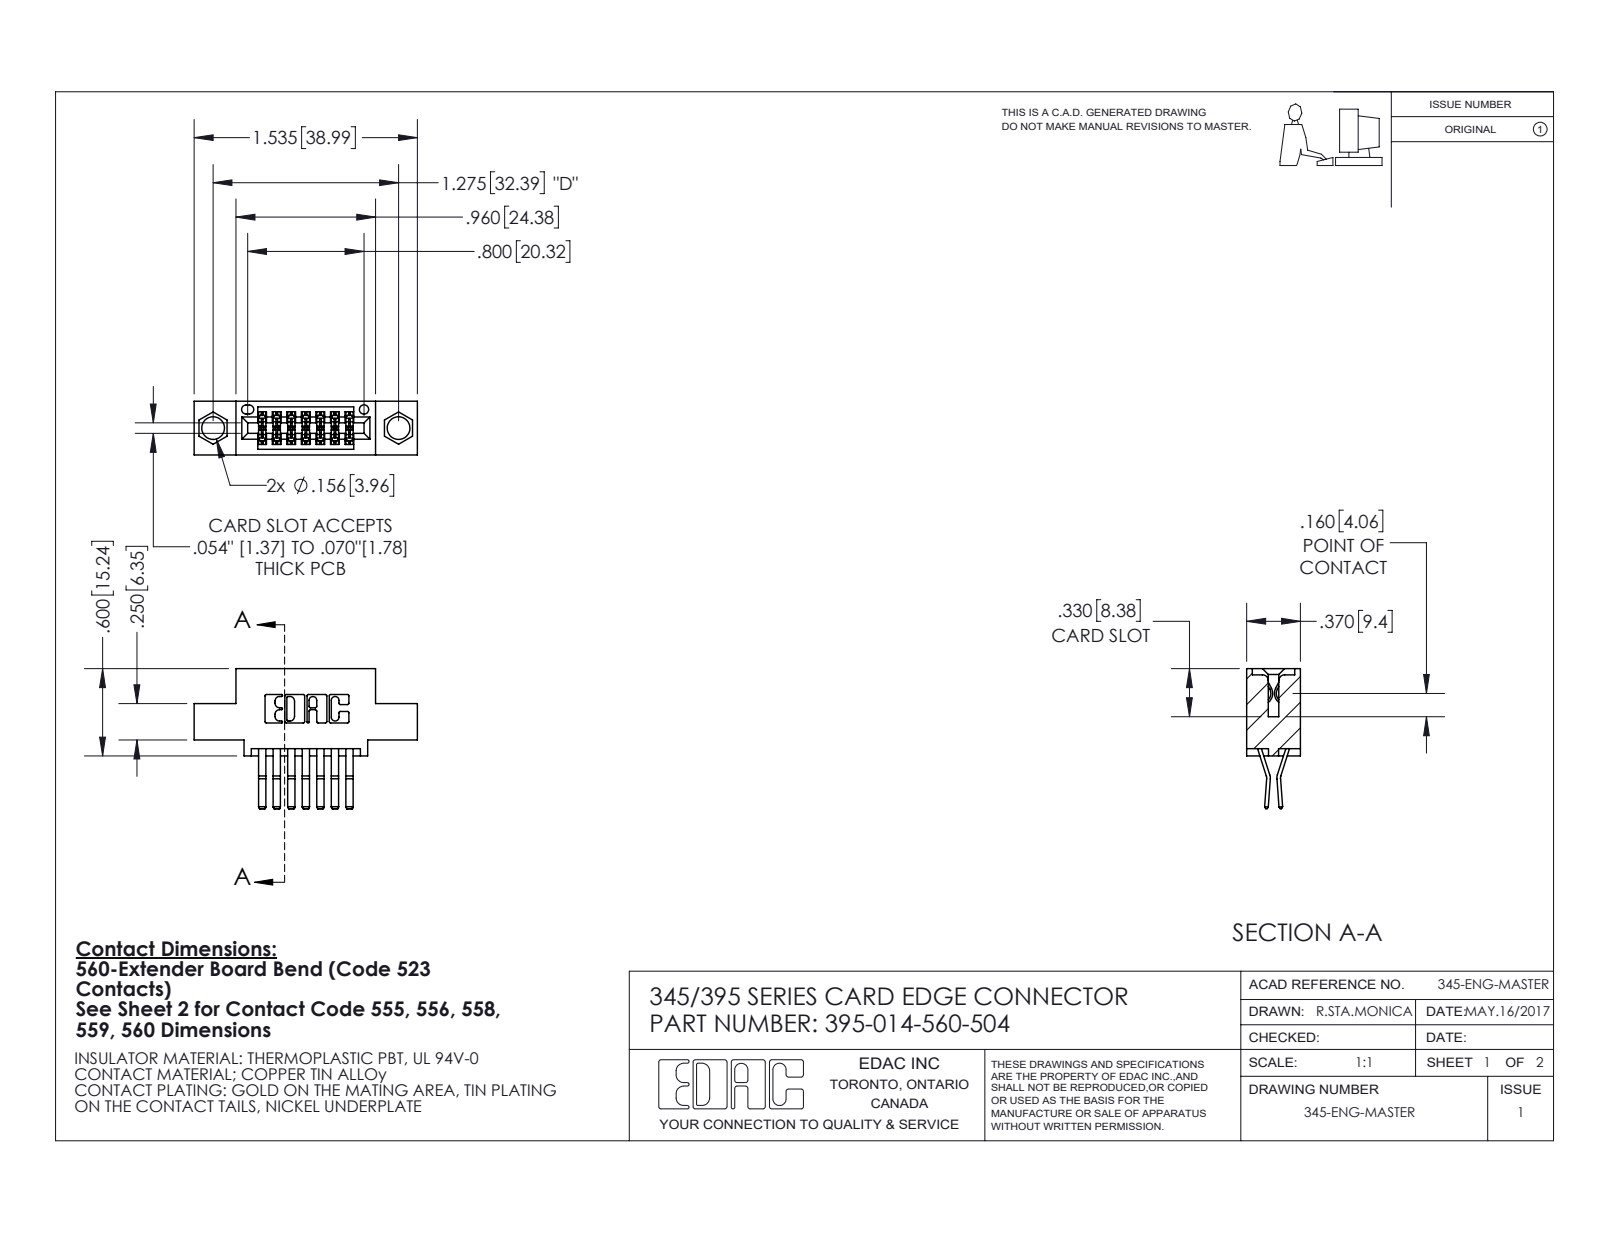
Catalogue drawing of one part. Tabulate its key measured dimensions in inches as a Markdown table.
| quantity | value |
| --- | --- |
| part name | 345 Part_0.110 Offset - 0.156 Dia-TI; 395-014-560-504; 345-292-001_560 Tail |
| STEP written by | SolidWorks 2020 (CONFIG_CONTROL_DESIGN) |
| units | inches |
| bodies | 15 solids, 872 faces (560 planar, 312 cylindrical, 0 other) |
| overall size | 1.535 × 0.962 × 0.37 |
| volume | 0.206 in³ |
| surface area | 6.962 in² |
| round holes (diameter × count) | 0.156 × 2, 0.064 × 1 |
| partial cylindrical surfaces (radius × count) | 0.01 × 22, 0.006 × 21, 0.007 × 6, 0.031 × 6, 0.026 × 3, 0.01 × 2, 0.014 × 2, 0.019 × 2 |
| main face-to-face distances | 0.2, 0.025, 0.298, 0.072, 0.37, 0.1, 0.3, 0.098, 0.272, 0.16 |
| hole center spacings | 0.27, 1.045, 1.275 |
